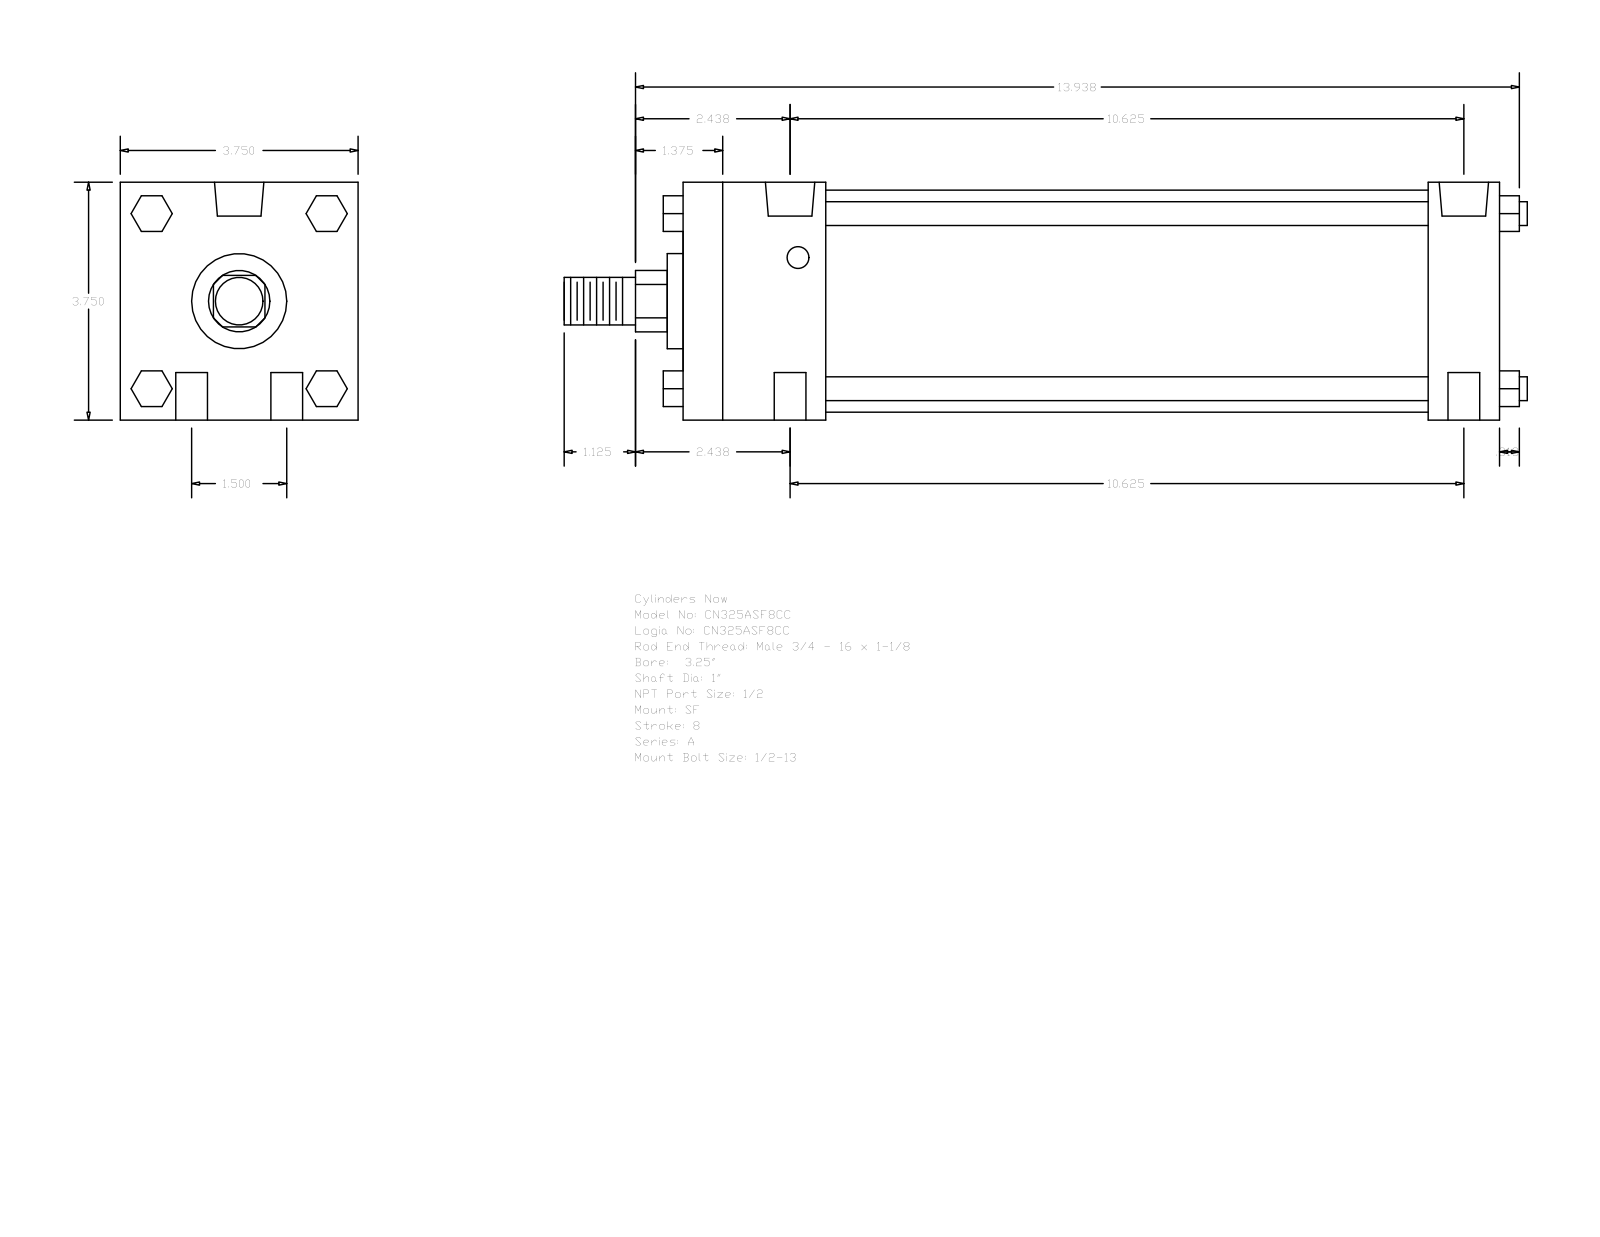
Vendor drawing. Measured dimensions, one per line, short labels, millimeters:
name: A_SF__0325_1
written by: GSSL Pune (CONFIG_CONTROL_DESIGN)
unit: mm
bodies: 0 solids, 124 faces (94 planar, 30 cylindrical, 0 other)
size: 385.76 × 95.25 × 95.25
holes: 4× ⌀12.7, 2× ⌀8.73, 2× ⌀19.77
bosses: 4× ⌀9.53, 1× ⌀88.9, 1× ⌀38.1, 1× ⌀25.4, 1× ⌀19.05
rounds: 1× R12.29
face distances: 95.24, 327.02, 28.57, 298.45, 57.15, 241.3, 269.87, 14.28, 35.05, 60.71
hole spacings: 19.05, 270.55, 269.88, 38.1, 272.56, 263.52
